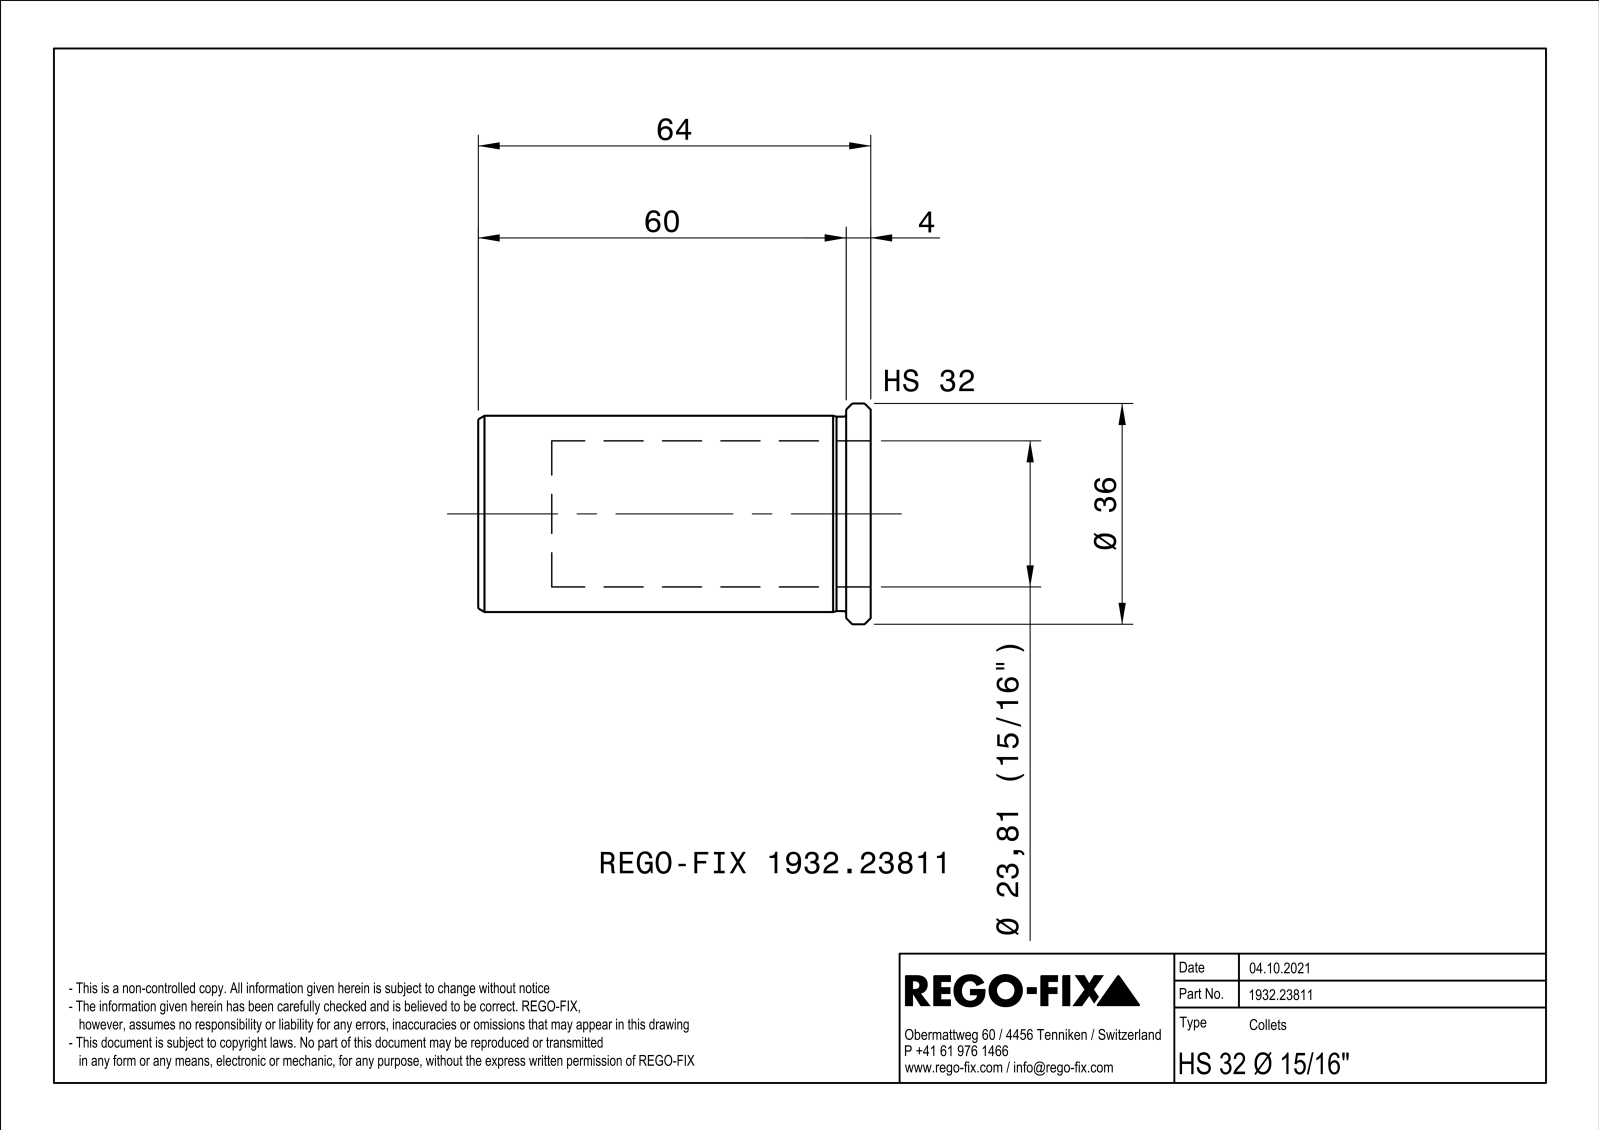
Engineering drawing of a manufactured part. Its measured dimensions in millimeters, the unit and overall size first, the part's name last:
Units: millimetres
Overall size (bounding box): 64 × 35.99 × 35.99
Round holes (diameter × count): ⌀23.81 ×1, ⌀26.5 ×1
Round bosses / shafts (diameter × count): ⌀36 ×1, ⌀32 ×1, ⌀31.7 ×1
Main face-to-face distances: 1, 64, 4, 60
Volume: 21 634 mm³ · Surface area: 13 429 mm²
Bodies: 1 solid, 70 faces (22 planar, 11 cylindrical, 37 other)
Part name (STEP PRODUCT): NOCUT
STEP written by: SIEMENS PLM Software Solid Edge ST10 (AUTOMOTIVE_DESIGN)
